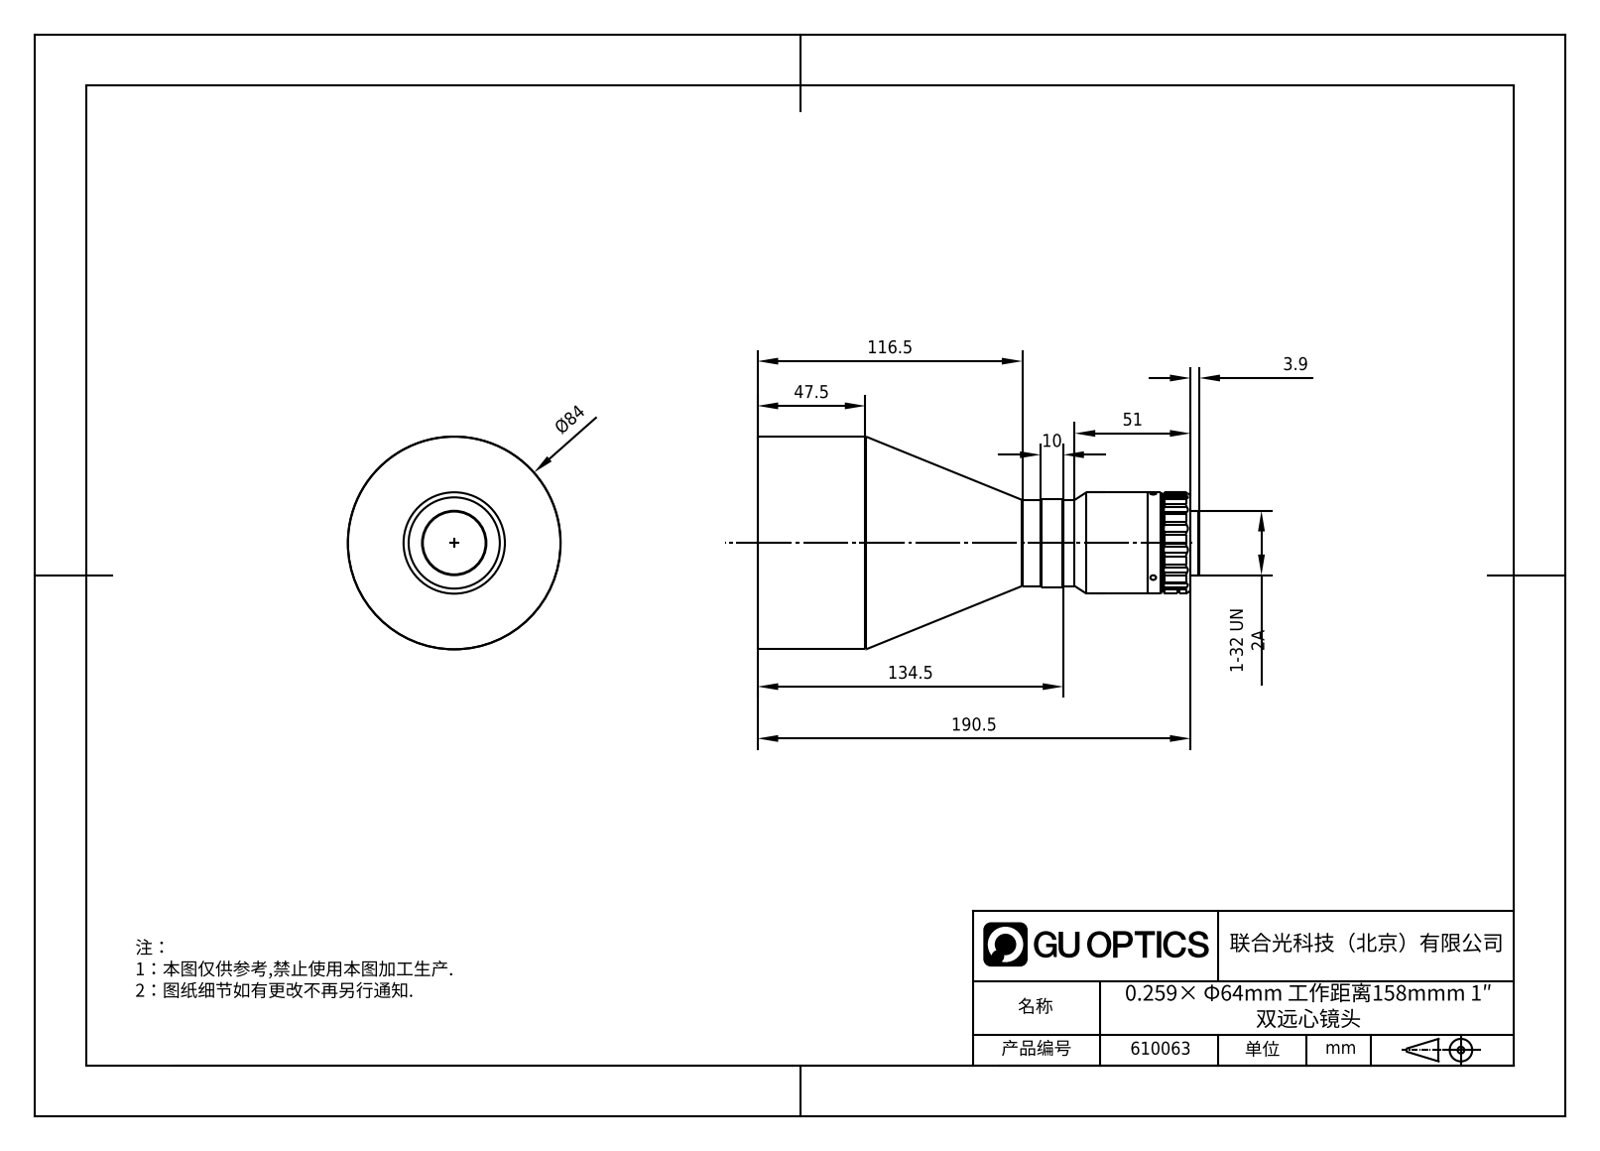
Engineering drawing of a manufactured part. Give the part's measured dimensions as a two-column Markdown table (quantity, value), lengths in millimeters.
| quantity | value |
| --- | --- |
| part name | DTCM110-64H-AL |
| STEP written by | SolidWorks 2017 (CONFIG_CONTROL_DESIGN) |
| units | millimeters |
| bodies | 1 solid, 51 faces (5 planar, 22 cylindrical, 24 other) |
| overall size | 194.4 × 84 × 84 |
| volume | 548 954 mm³ |
| surface area | 43 355 mm² |
| round holes (diameter × count) | 2.5 × 3 |
| round bosses / shafts (diameter × count) | 84 × 1, 40 × 1, 35 × 1, 34 × 1, 29 × 1, 25.4 × 1 |
| main face-to-face distances | 171.6, 172.1, 0.5, 190.5, 18.9, 18.4, 194.4, 22.8, 22.3, 3.9 |
